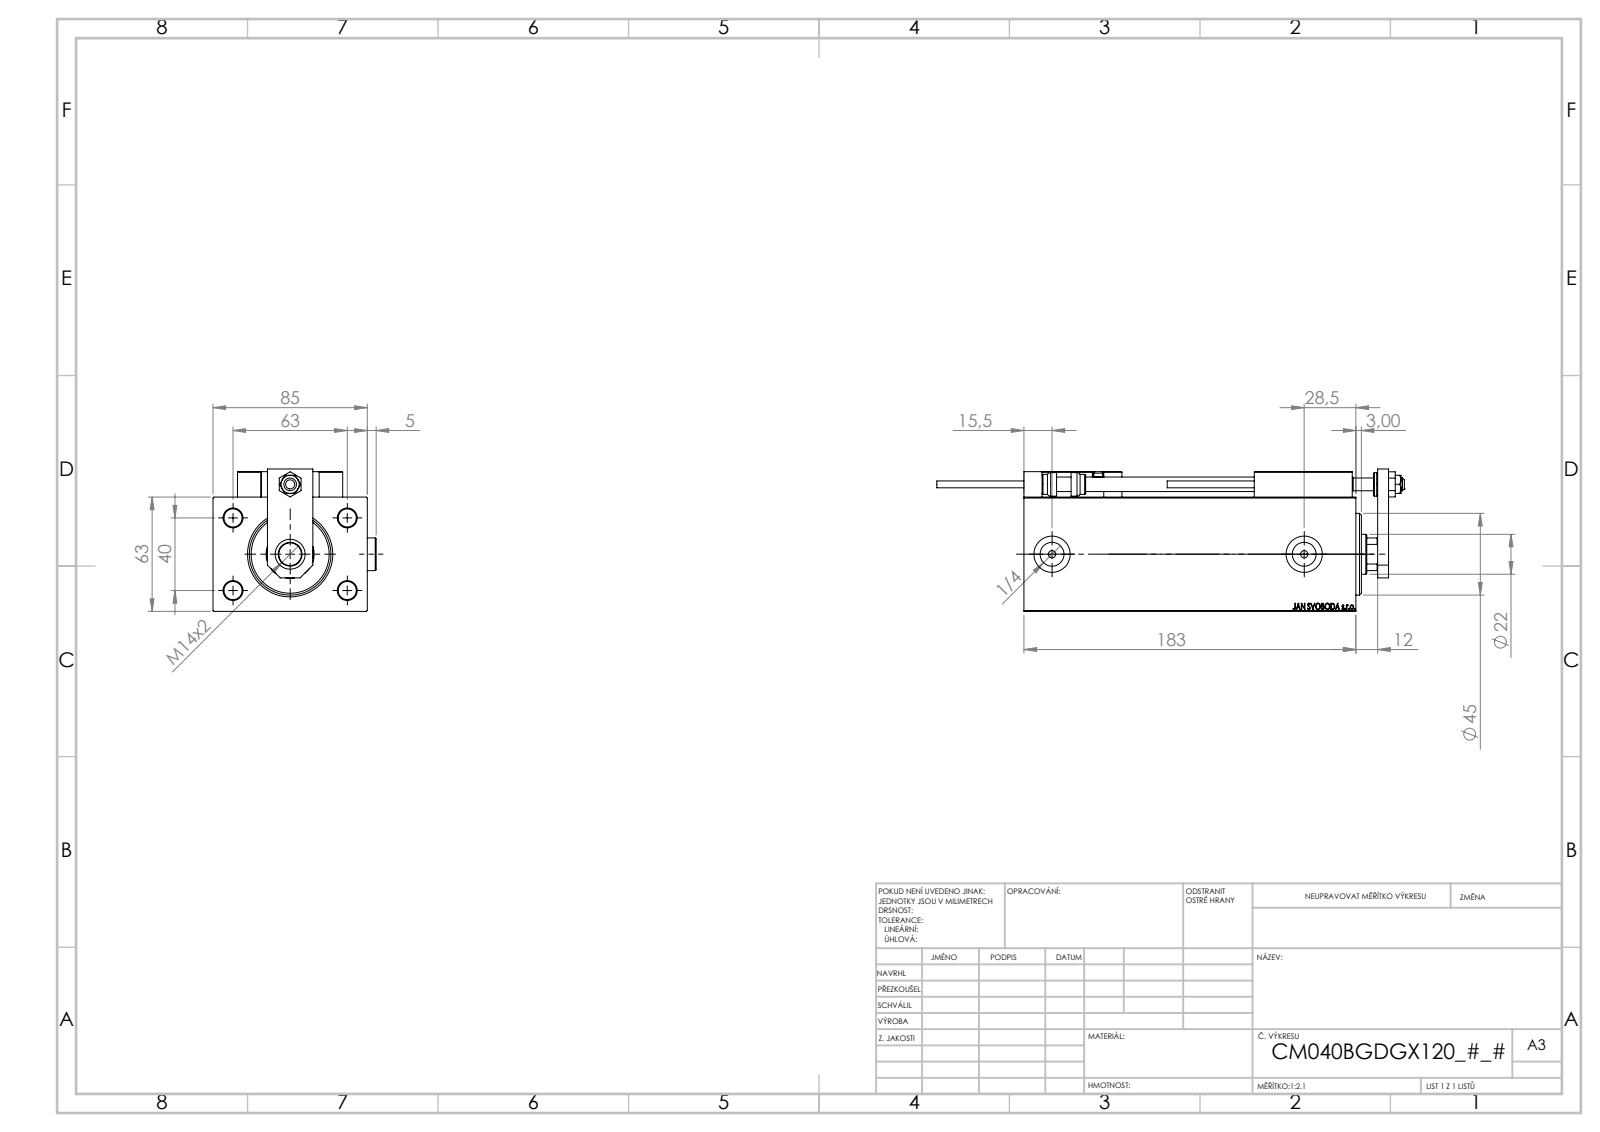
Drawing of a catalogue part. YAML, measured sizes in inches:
part_name: "Block; SWITCH DIM B,W; TYC_L79; NUT_D10 (+7 more)"
step_written_by: "SolidWorks 2019 (CONFIG_CONTROL_DESIGN)"
units: inches
bodies: {solids: 26, faces: 1372, planar: 595, cylindrical: 200, other: 577}
overall_size: [10.146, 3.539, 3.091]
volume: 55.81
surface_area: 227
round_holes:
  - {diameter: 0.157, count: 6}
  - {diameter: 0.315, count: 5}
  - {diameter: 0.126, count: 4}
  - {diameter: 0.394, count: 4}
  - {diameter: 0.197, count: 2}
  - {diameter: 0.518, count: 2}
  - {diameter: 0.787, count: 2}
  - {diameter: 0.276, count: 1}
  - {diameter: 0.492, count: 1}
  - {diameter: 0.65, count: 1}
  - {diameter: 0.866, count: 1}
  - {diameter: 1.004, count: 1}
round_bosses_or_shafts:
  - {diameter: 0.709, count: 2}
  - {diameter: 0.197, count: 2}
  - {diameter: 0.15, count: 2}
  - {diameter: 0.512, count: 1}
  - {diameter: 0.433, count: 1}
partial_cylinders:
  - {radius: 0.012, count: 30}
  - {radius: 0.118, count: 2}
  - {radius: 0.413, count: 1}
face_to_face_distances: [2.48, 3.346, 0.472, 7.205, 6.732, 0.551, 3.031, 0.709, 1.181, 0.531]
hole_center_spacings: [1.469, 0.448, 0.787, 1.165, 1.169, 1.42, 1.438, 1.575]
